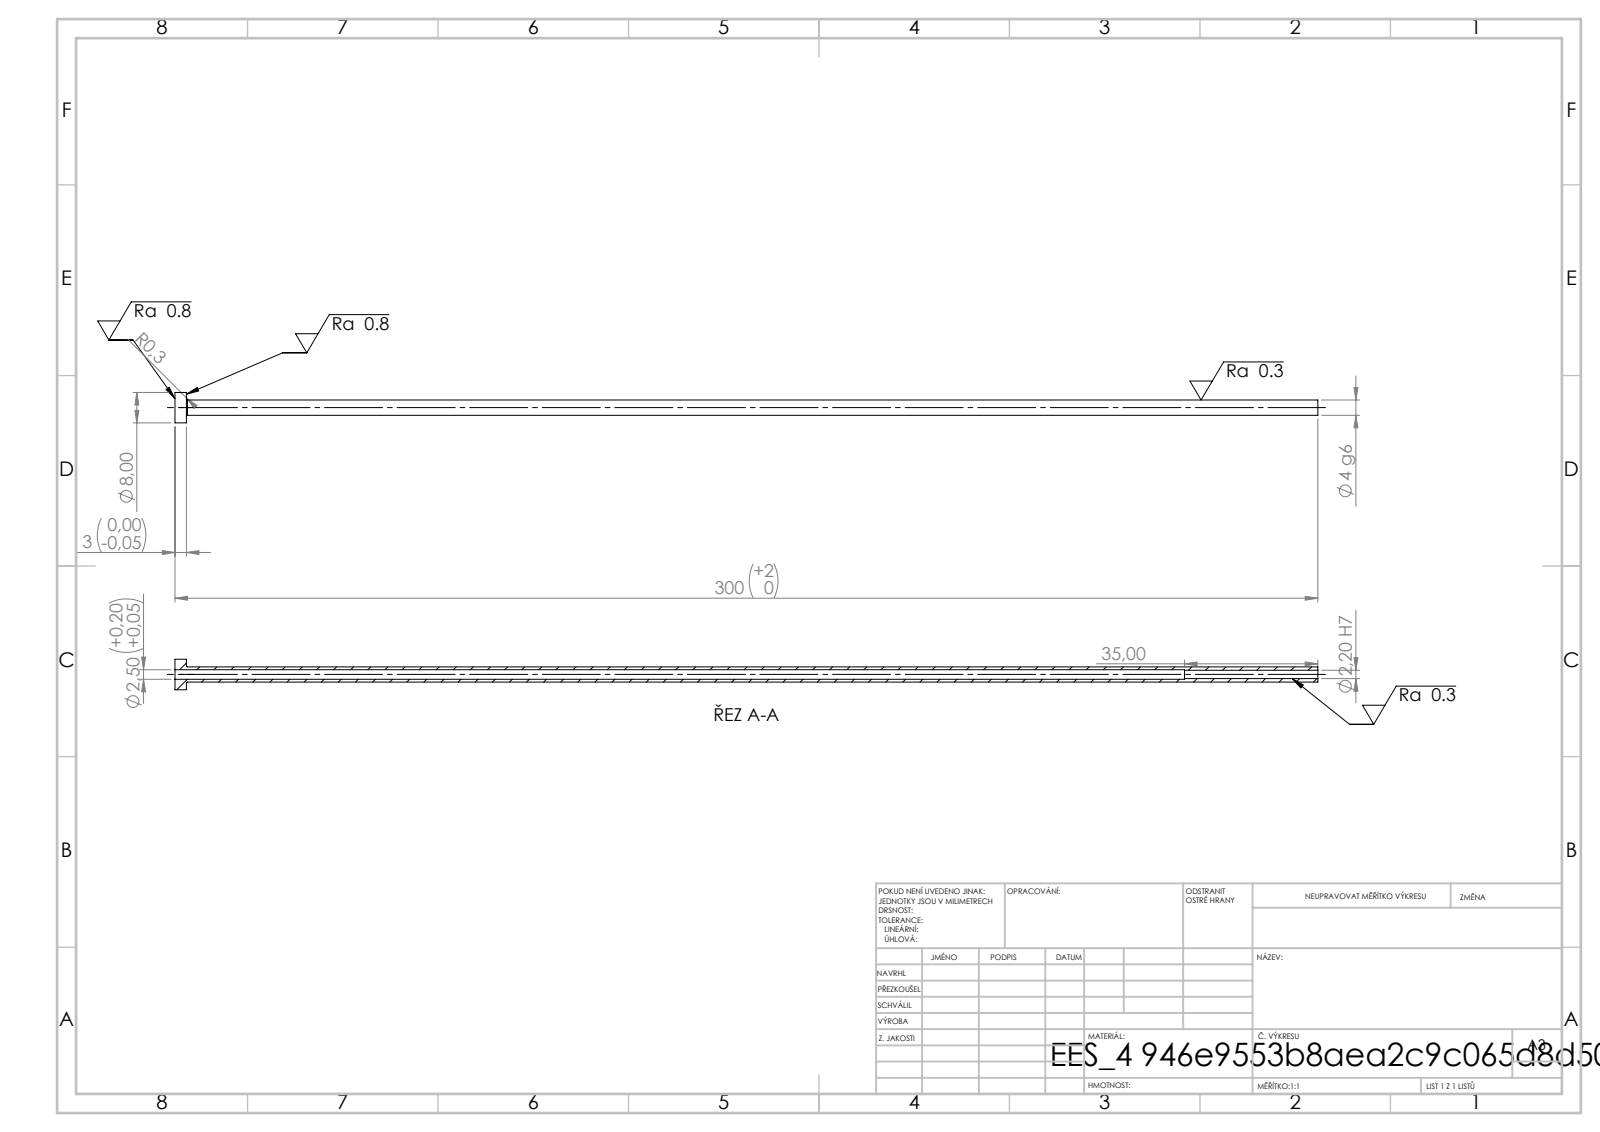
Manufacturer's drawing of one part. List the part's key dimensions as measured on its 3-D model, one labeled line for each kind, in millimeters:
STEP written by: SolidWorks 2019 (CONFIG_CONTROL_DESIGN)
Units: millimetres
Bodies: 1 solid, 14 faces (4 planar, 8 cylindrical, 2 other)
Overall size (bounding box): 300 × 8 × 8
Volume: 2 449 mm³ · Surface area: 6 222 mm²
Round holes (diameter × count): ⌀2.2 ×1, ⌀2.5 ×1
Round bosses / shafts (diameter × count): ⌀8 ×1, ⌀4 ×1
Main face-to-face distances: 3, 300, 297, 265, 262, 35
